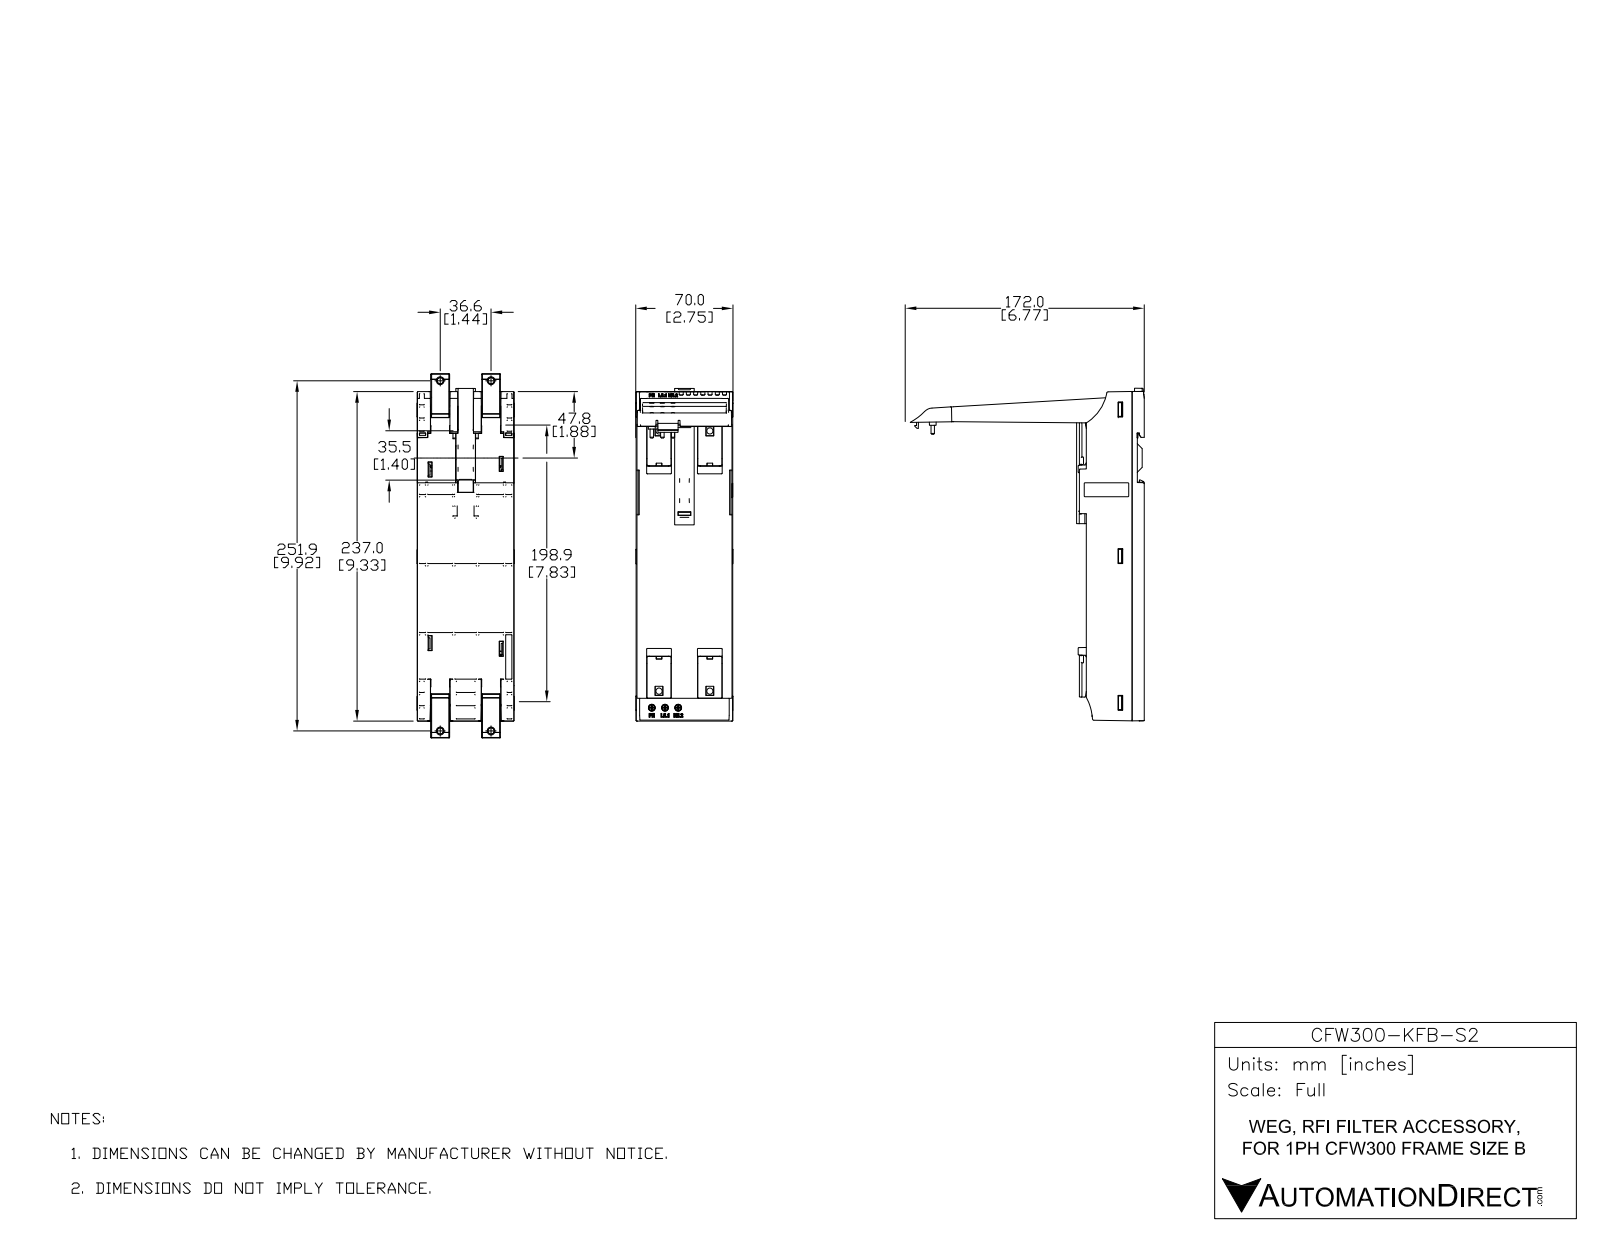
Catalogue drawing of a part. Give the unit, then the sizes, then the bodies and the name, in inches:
Units: inches
Overall size (bounding box): 9.424 × 6.628 × 2.756
Round holes (diameter × count): ⌀0.098 ×6, ⌀0.118 ×3, ⌀0.189 ×3
Round bosses / shafts (diameter × count): ⌀0.039 ×3
Partial cylindrical surfaces — rounded edges, fillets, slot ends (radius × count): R0.012 ×831, R0.02 ×351, R0.059 ×22, R0.039 ×18, R0.089 ×6, R0.017 ×4, R0.13 ×3, R0.043 ×1
Main face-to-face distances: 0.087, 1.358, 1.445, 1.272, 0.197, 0.283, 1.642, 1.555, 1.441, 0.079
Hole centre spacings: 0.3, 5.279, 0.6, 5.27, 0.374, 5.304, 0.748, 8.31
Volume: 11.16 in³ · Surface area: 290.4 in²
Bodies: 18 solids, 5086 faces (1841 planar, 1849 cylindrical, 1396 other)
Part name (STEP PRODUCT): CFW300-KFB
STEP written by: SolidWorks 2017 (AUTOMOTIVE_DESIGN)
